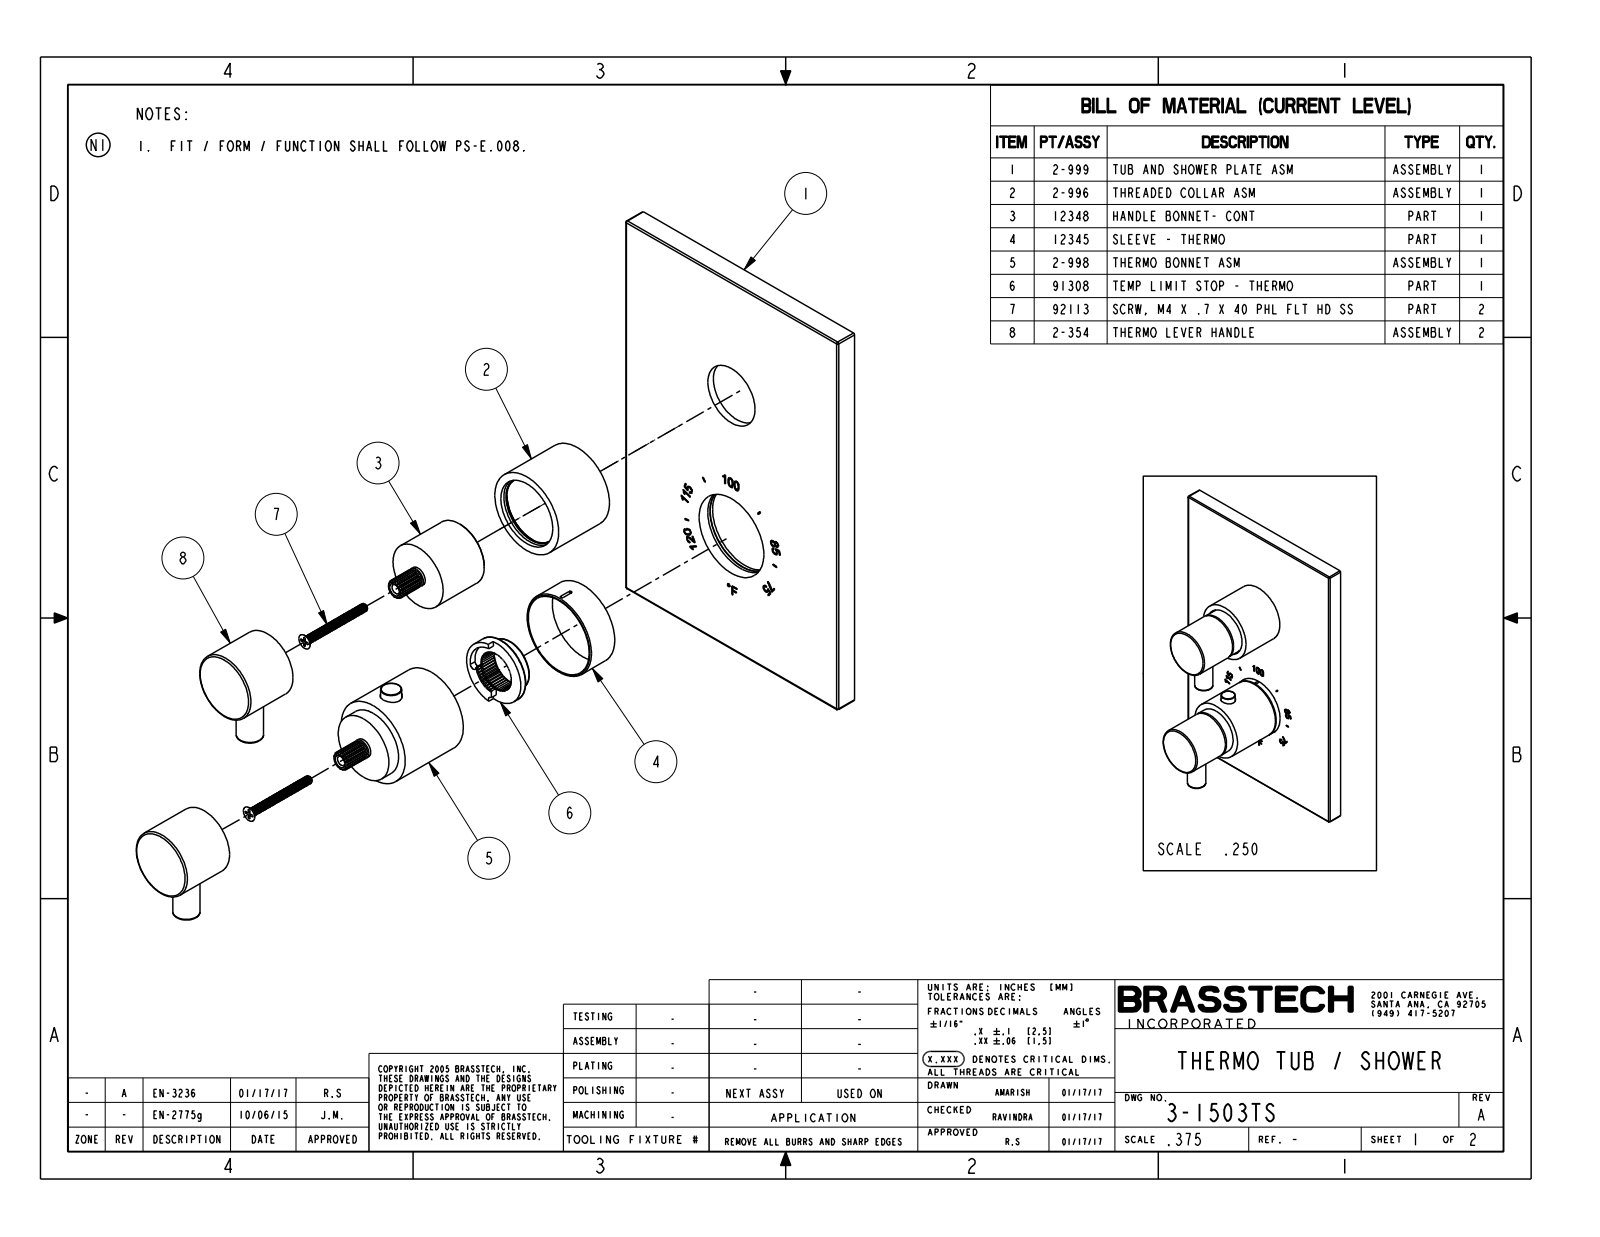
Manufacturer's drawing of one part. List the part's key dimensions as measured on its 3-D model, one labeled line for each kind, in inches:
Part name (STEP PRODUCT): 12349_AF1; H-78_2_FEET_AF12; 91678; 2-999_AF1_ASM (+8 more)
STEP written by: PRO/ENGINEER BY PARAMETRIC TECHNOLOGY CORPORATION, 2013150 (CONFIG_CONTROL_DESIGN)
Units: inches
Bodies: 24 solids, 2305 faces (837 planar, 683 cylindrical, 785 other)
Overall size (bounding box): 8.25 × 5.5 × 4.218
Volume: 12.02 in³ · Surface area: 373.3 in²
Round holes (diameter × count): ⌀0.19 ×2, ⌀0.196 ×2, ⌀0.25 ×2, ⌀0.276 ×2, ⌀0.301 ×2, ⌀0.339 ×2, ⌀0.52 ×2, ⌀0.063 ×1, ⌀0.079 ×1, ⌀0.1 ×1, ⌀0.126 ×1, ⌀0.406 ×1
Round bosses / shafts (diameter × count): ⌀0.157 ×3, ⌀1.654 ×2, ⌀1.312 ×2, ⌀0.512 ×2, ⌀0.5 ×2, ⌀0.453 ×2, ⌀0.4 ×2, ⌀0.37 ×2
Partial cylindrical surfaces — rounded edges, fillets, slot ends (radius × count): R0.03 ×8, R0.5 ×8, R0.039 ×2, R0.075 ×2, R0.082 ×2, R0.125 ×2, R0.164 ×2, R0.187 ×2
Main face-to-face distances: 0.08, 0.168, 0.248, 0.08, 0.25, 0.33, 5.5, 0.37, 5.42, 0.19
Hole centre spacings: 0.37, 0.554, 0.854, 1.144, 1.224, 1.696, 2.596, 2.596
